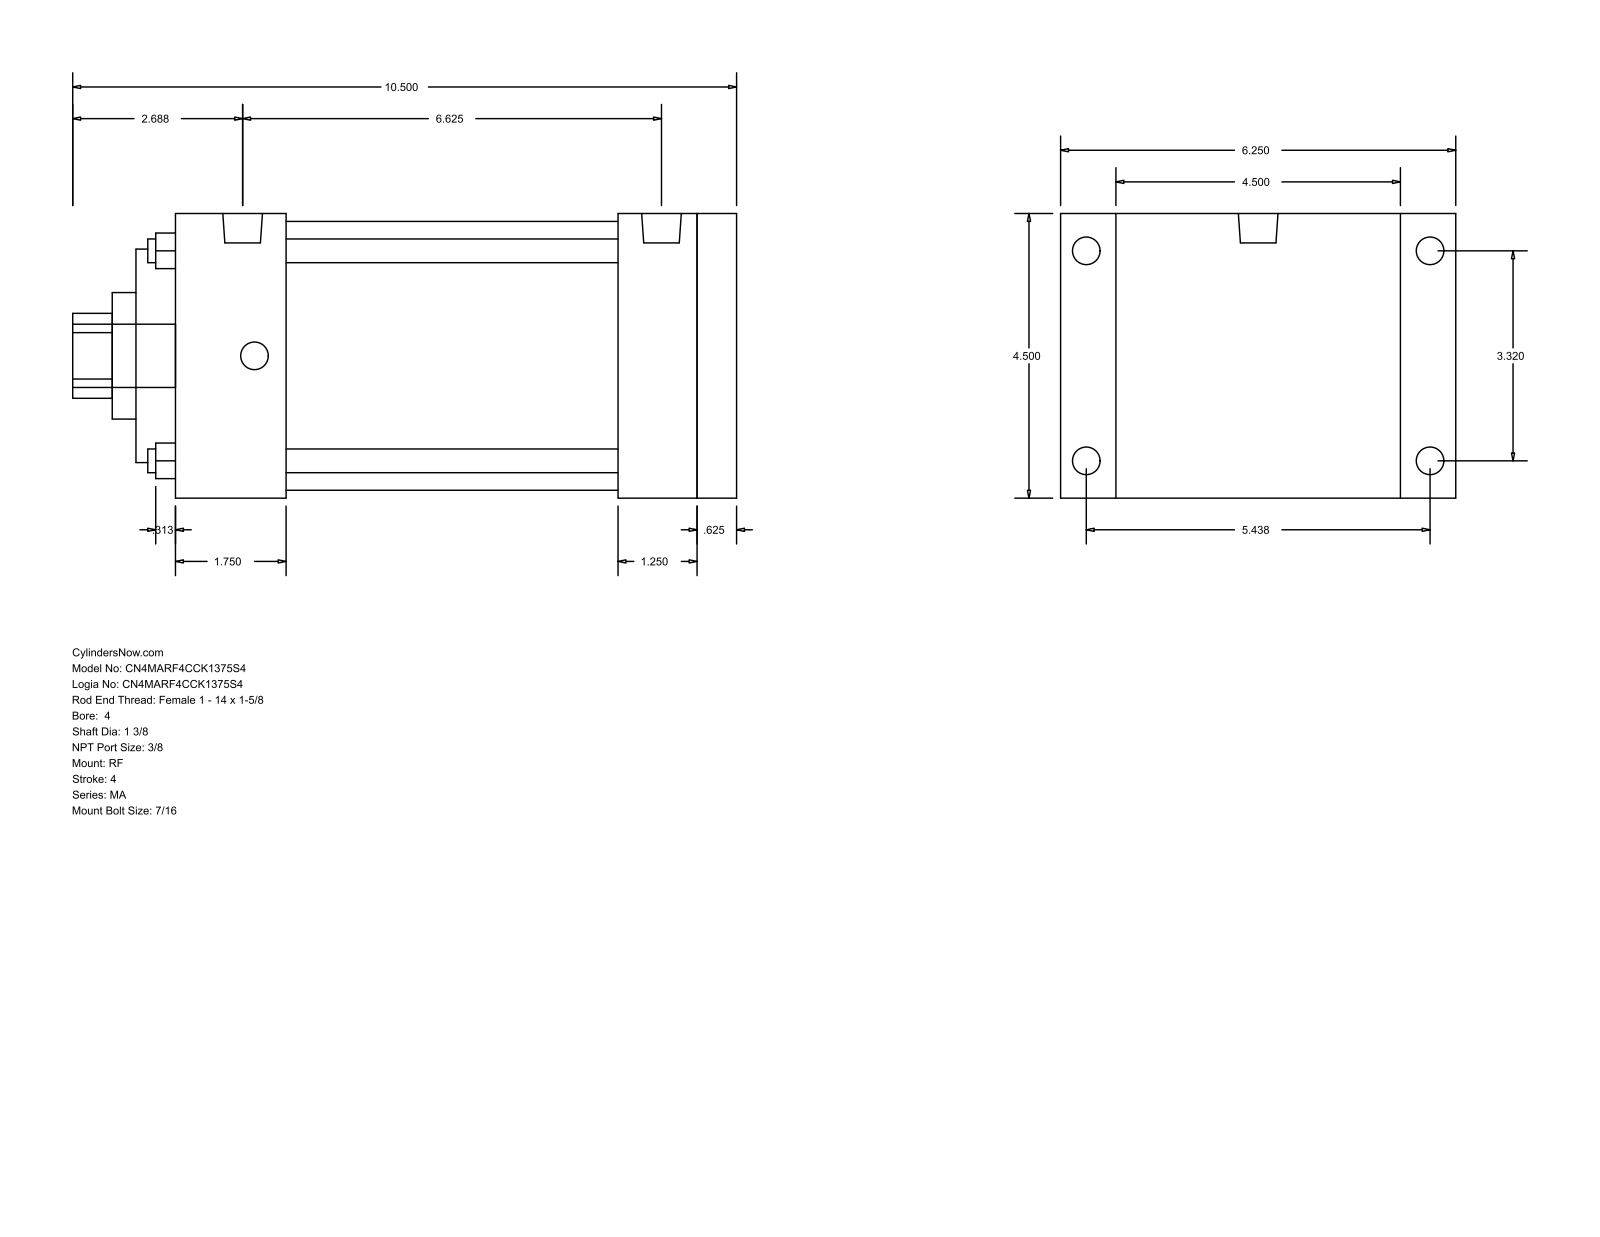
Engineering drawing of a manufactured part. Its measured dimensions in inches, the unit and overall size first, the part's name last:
Units: inches
Overall size (bounding box): 10.5 × 6.25 × 4.5
Round holes (diameter × count): ⌀0.375 ×4, ⌀1.375 ×1, ⌀2 ×1, ⌀3.375 ×1, ⌀4.25 ×1
Round bosses / shafts (diameter × count): ⌀0.437 ×8, ⌀0.627 ×2, ⌀1 ×1
Partial cylindrical surfaces — rounded edges, fillets, slot ends (radius × count): R0.672 ×1
Main face-to-face distances: 4.5, 8.875, 0.625, 8.25, 0.625, 8.875, 9.5, 0.875, 5.375, 7.625
Hole centre spacings: 2.347, 3.32, 4.695
Bodies: 0 solids, 94 faces (65 planar, 29 cylindrical, 0 other)
Part name (STEP PRODUCT): MA_RF__0400_1.375
STEP written by: GSSL Pune (CONFIG_CONTROL_DESIGN)
